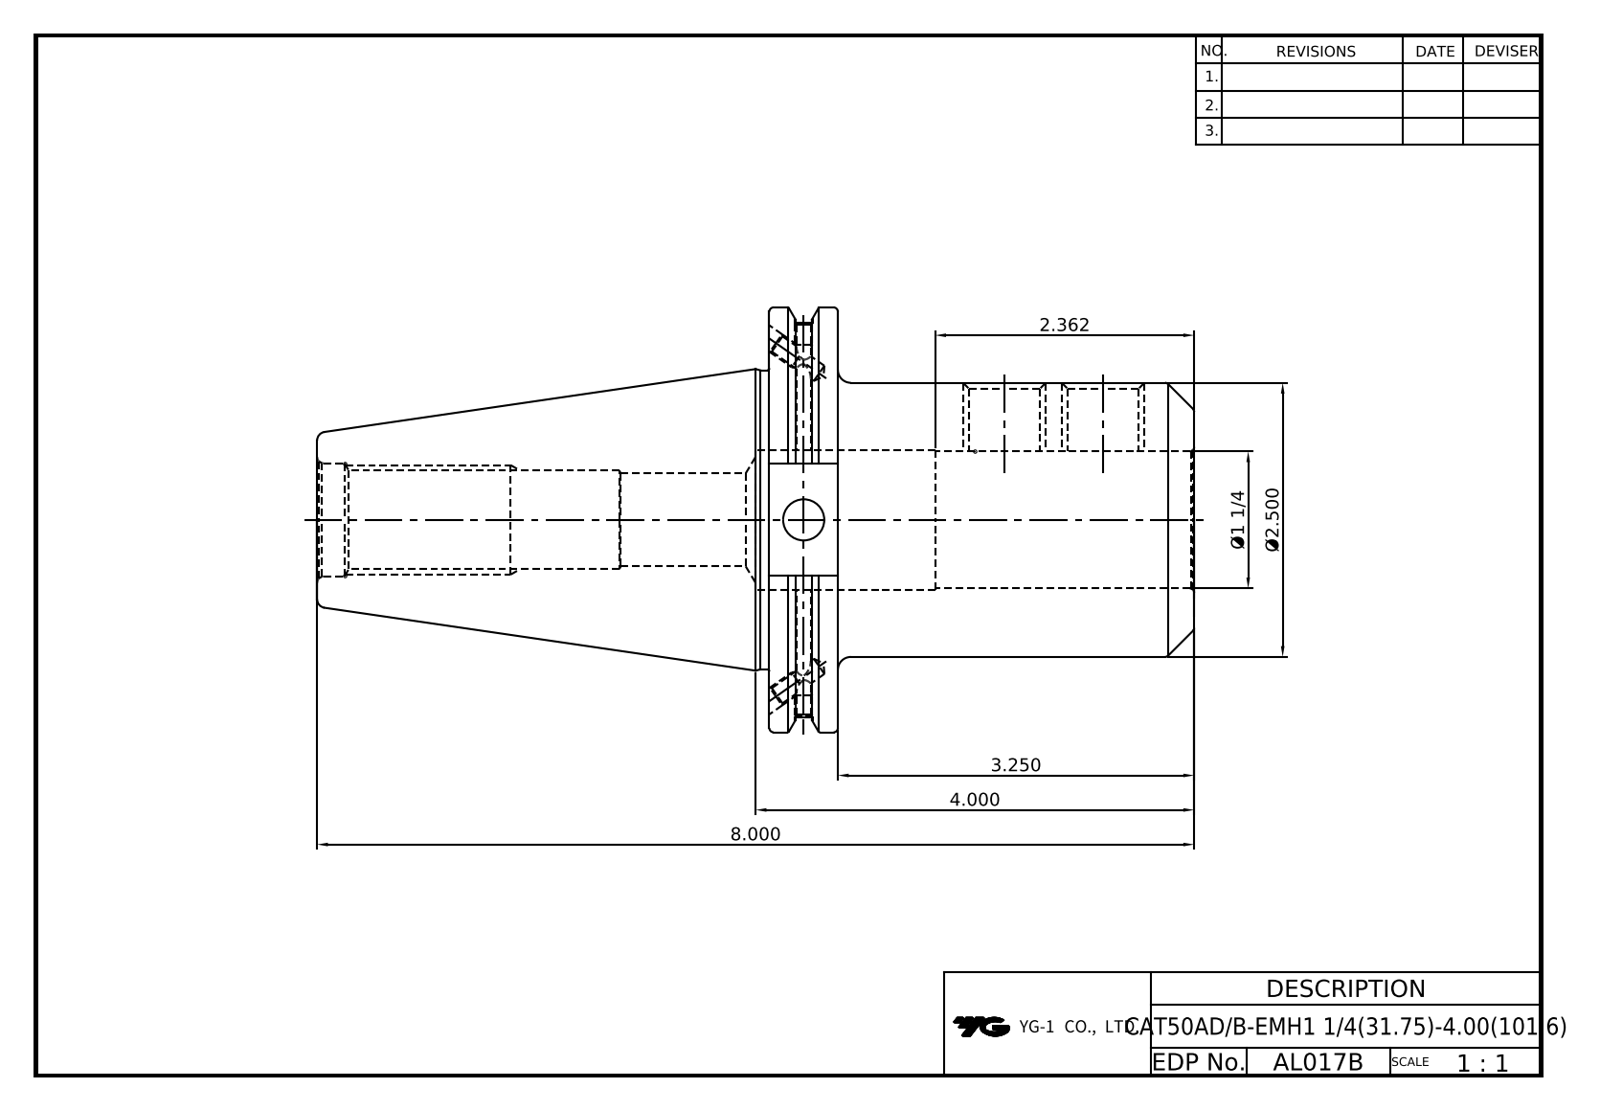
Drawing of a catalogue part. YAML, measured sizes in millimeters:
part_name: "LO-CAT50ADB-EMH31.75-101.6"
step_written_by: "Autodesk Inventor 2022 (AUTOMOTIVE_DESIGN)"
units: millimeters
bodies: {solids: 1, faces: 91, planar: 39, cylindrical: 28, other: 24}
overall_size: [203.2, 98.42, 94.69]
volume: 493104
surface_area: 69768
round_holes:
  - {diameter: 3.24, count: 2}
  - {diameter: 4.13, count: 2}
  - {diameter: 4.2, count: 2}
  - {diameter: 5, count: 2}
  - {diameter: 17.32, count: 2}
  - {diameter: 9.53, count: 1}
  - {diameter: 21.5, count: 1}
  - {diameter: 21.97, count: 1}
  - {diameter: 26.2, count: 1}
  - {diameter: 31.75, count: 1}
  - {diameter: 32.95, count: 1}
round_bosses_or_shafts:
  - {diameter: 98.42, count: 1}
  - {diameter: 91.29, count: 1}
  - {diameter: 69.25, count: 1}
  - {diameter: 63.5, count: 1}
face_to_face_distances: [15.88, 98.43, 82.55, 101.6, 104.77, 120.65, 203.2, 3.17, 19.05, 73.03]
hole_center_spacings: [22.86]
